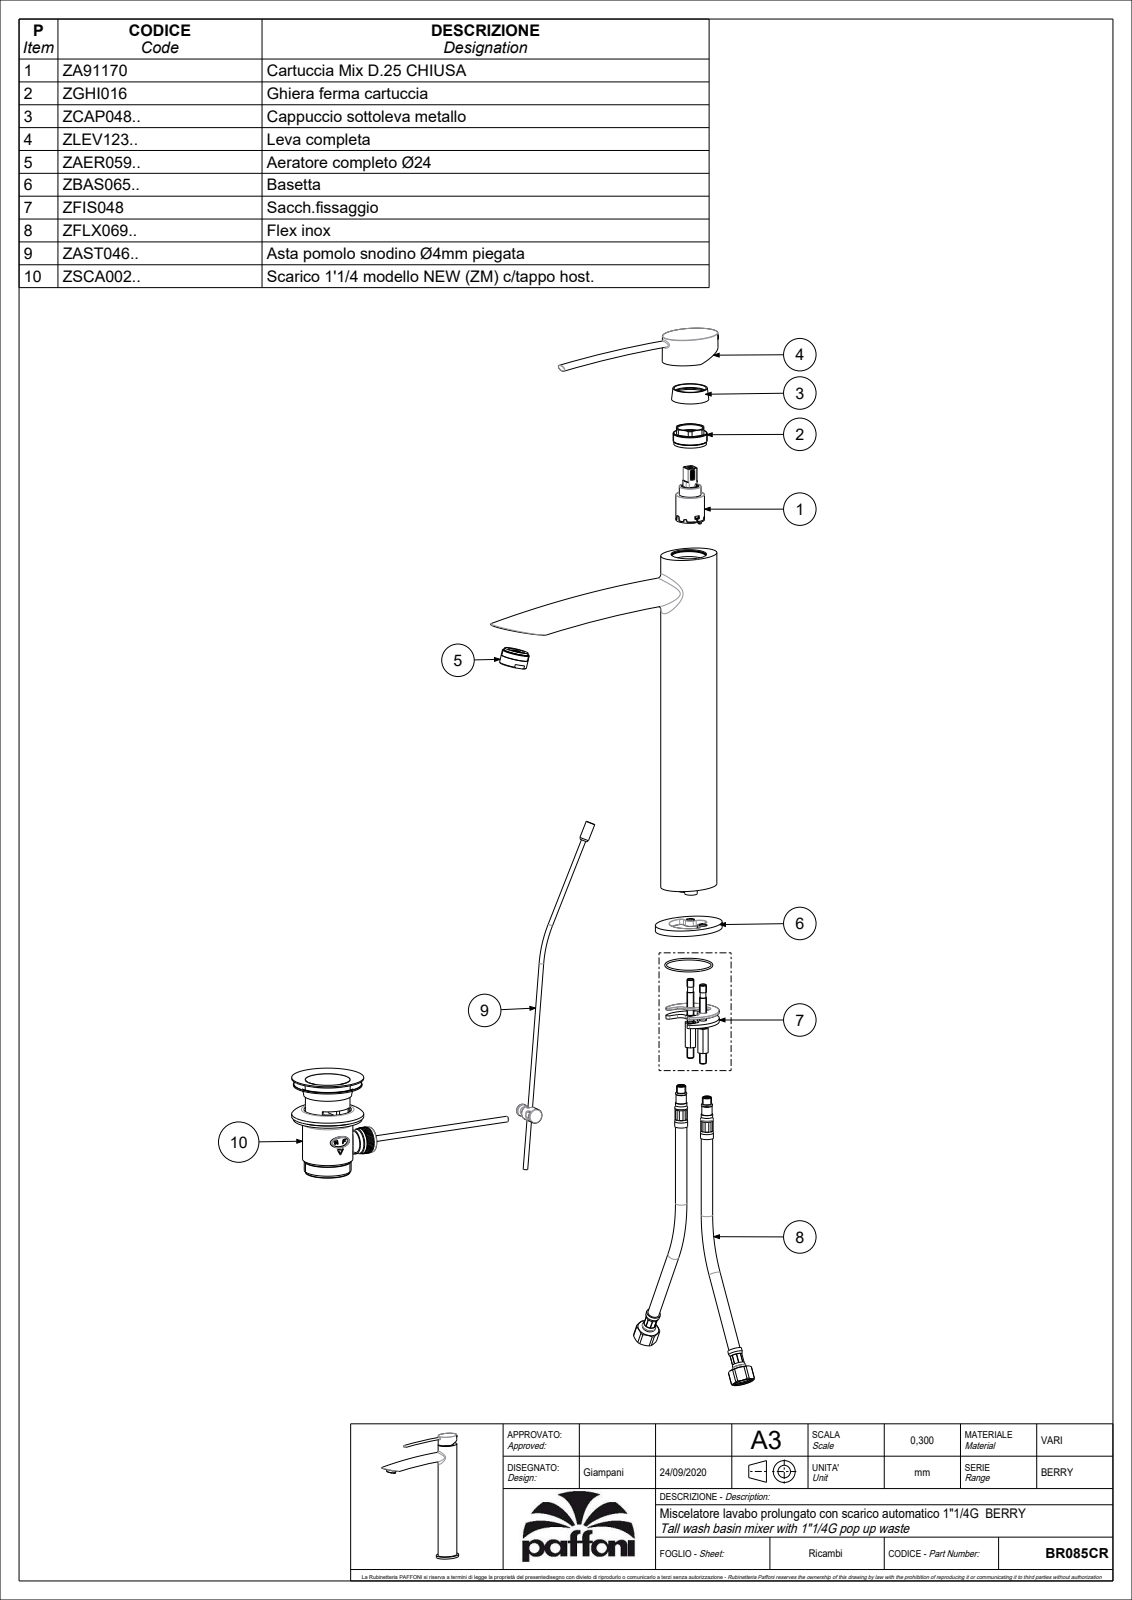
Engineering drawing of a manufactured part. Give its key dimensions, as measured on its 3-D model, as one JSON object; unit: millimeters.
{"part_name": "BR085CR", "step_written_by": "CREO PARAMETRIC BY PTC INC, 2020044 (CONFIG_CONTROL_DESIGN)", "units": "millimeters", "bodies": {"solids": 4, "faces": 2669, "planar": 1962, "cylindrical": 387, "other": 320}, "overall_size": [330.2, 249.53, 46], "volume_mm3": 253236, "surface_area_mm2": 167051, "round_holes": [[6, 4], [8.2, 4], [5, 3], [7, 3], [3, 2], [3.2, 2], [4, 2], [6.2, 2], [20, 2], [4.2, 1], [15, 1], [16, 1]], "round_bosses_or_shafts": [[8, 5], [5, 3], [11, 2], [6, 2], [4, 2], [3, 2], [38.8, 1], [28.5, 1]], "partial_cylinders_radius": [[0.5, 52], [1, 24], [0.3, 23], [0.2, 13], [0.15, 10], [2, 10], [1.5, 4], [2.45, 4]], "face_to_face_distances": [25, 5, 1, 6, 12, 274, 7, 19, 2, 327.9], "hole_center_spacings": [3.64, 4.24, 5.59, 6.36, 6.5, 8, 8.14, 9.43]}
